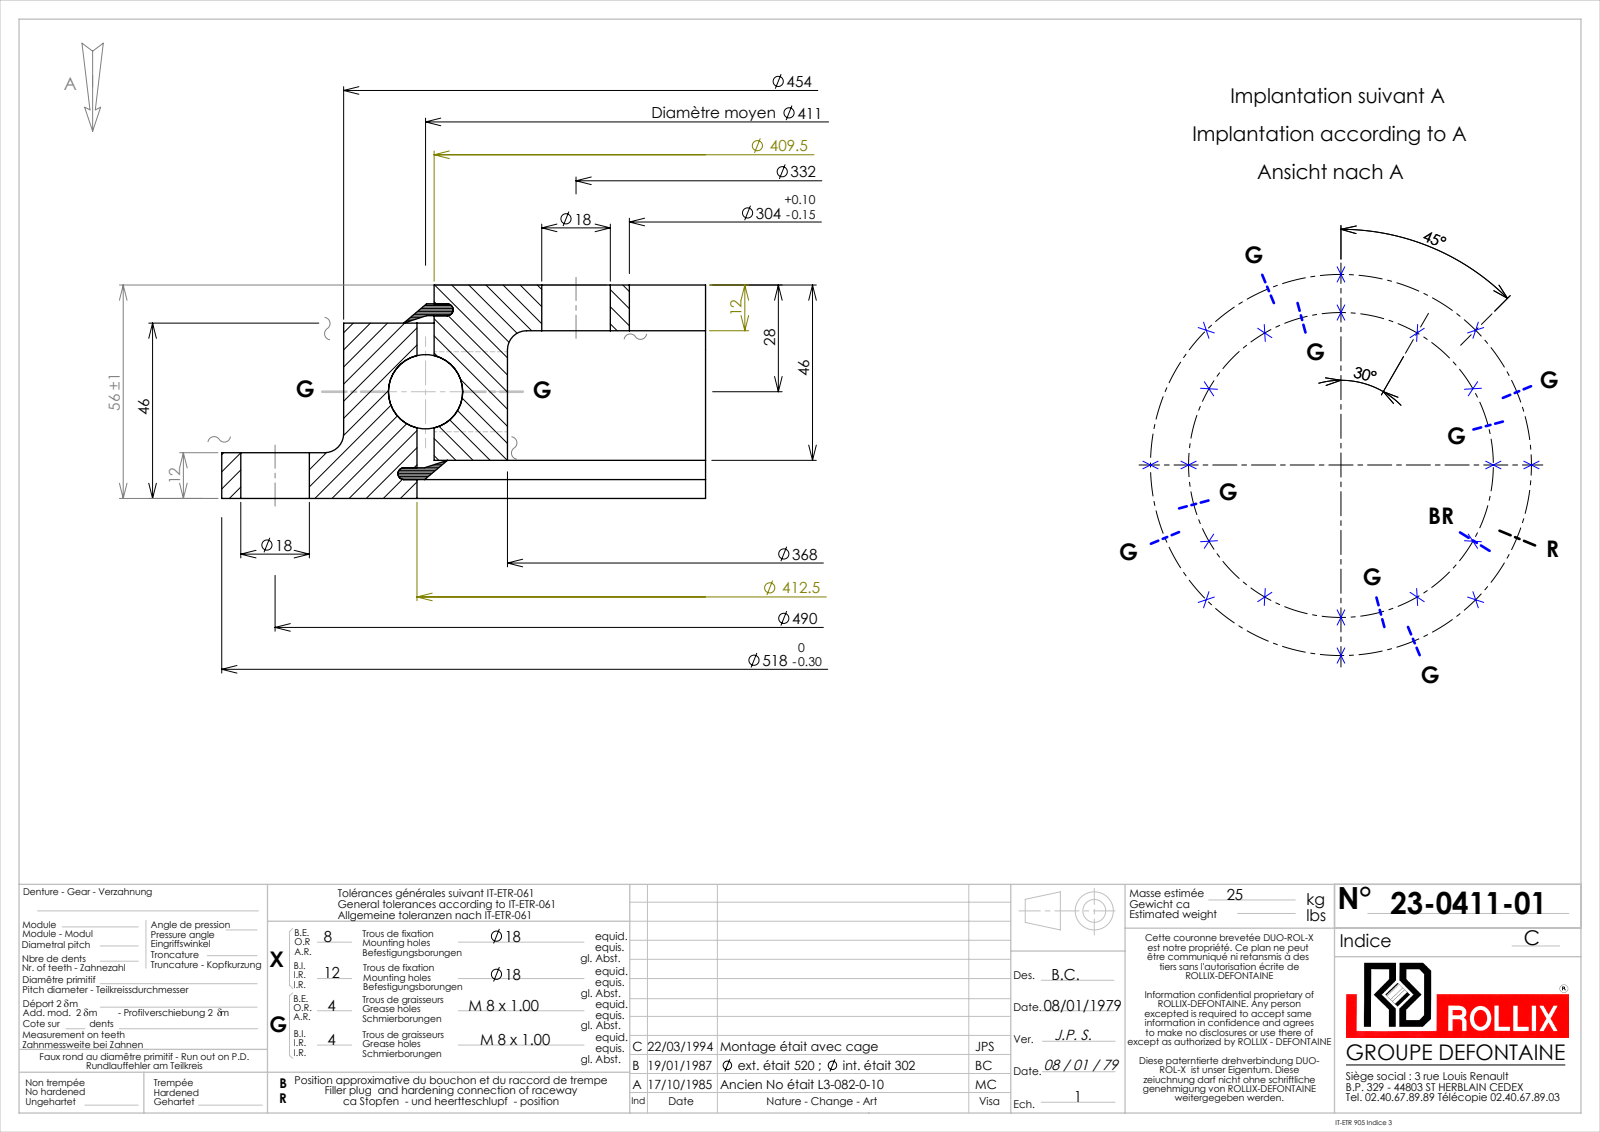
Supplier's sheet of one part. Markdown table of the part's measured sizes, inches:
| quantity | value |
| --- | --- |
| part name | 23-0411-01 |
| STEP written by | SolidWorks 2016 (CONFIG_CONTROL_DESIGN) |
| units | inches |
| bodies | 13 solids, 298 faces (94 planar, 92 cylindrical, 112 other) |
| overall size | 20.394 × 20.394 × 2.205 |
| volume | 183.3 in³ |
| surface area | 968.1 in² |
| round holes (diameter × count) | 0.709 × 20, 0.276 × 8, 11.969 × 1, 14.488 × 1, 16.358 × 1 |
| round bosses / shafts (diameter × count) | 0.315 × 8, 20.394 × 1, 17.874 × 1, 16.004 × 1 |
| main face-to-face distances | 0.472, 1.732, 2.205, 0.394, 1.811, 1.339, 0.079, 1.26, 1.417, 0.195 |
| hole center spacings | 6.535, 3.383, 9.243, 11.32, 12.626, 3.737, 5.154, 6.826 |
